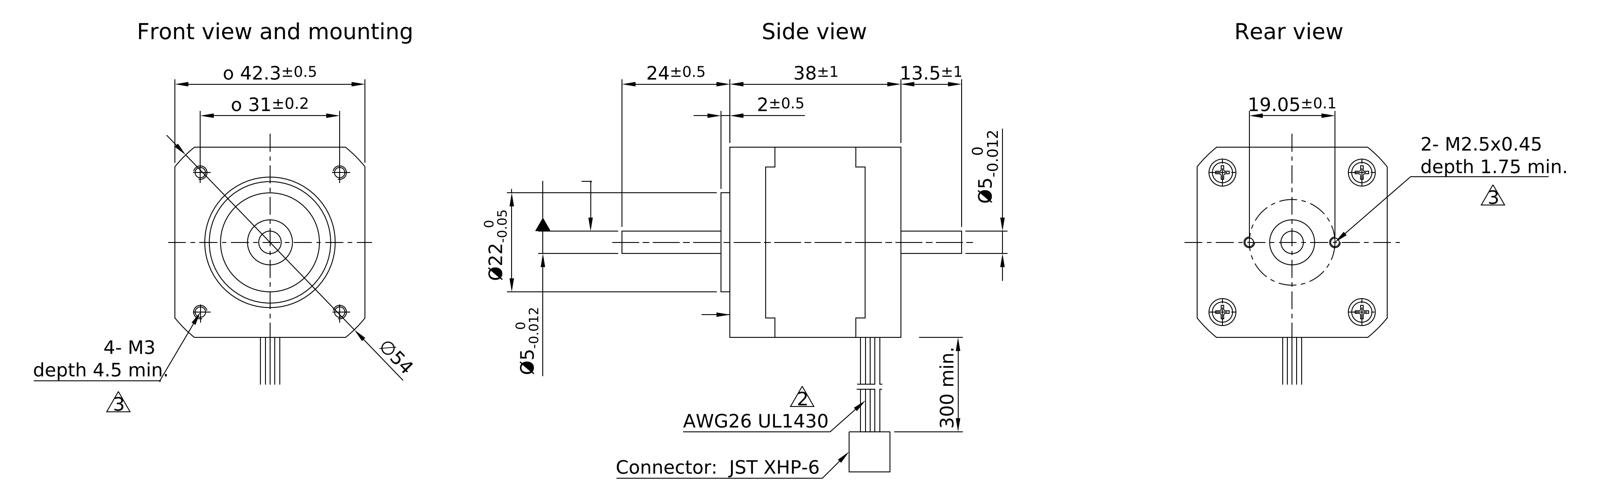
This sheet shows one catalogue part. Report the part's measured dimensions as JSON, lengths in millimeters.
{"part_name": "ST4118M..._B", "step_written_by": "Autodesk Inventor 2010 (AUTOMOTIVE_DESIGN)", "units": "millimeters", "bodies": {"solids": 0, "faces": 147, "planar": 83, "cylindrical": 35, "other": 29}, "overall_size": [75.5, 57, 42], "round_holes": [[6, 4], [2.01, 2], [2.46, 2], [2.46, 2], [7.5, 1]], "round_bosses_or_shafts": [[1, 4], [22, 1], [5, 1]], "partial_cylinders_radius": [[2, 8], [27, 1]], "face_to_face_distances": [42, 38, 2, 48.08, 40, 11, 27, 37.5, 0.5, 2.5], "hole_center_spacings": [16.61, 21.92, 29.44, 31, 9.53, 43.84, 19.06]}
